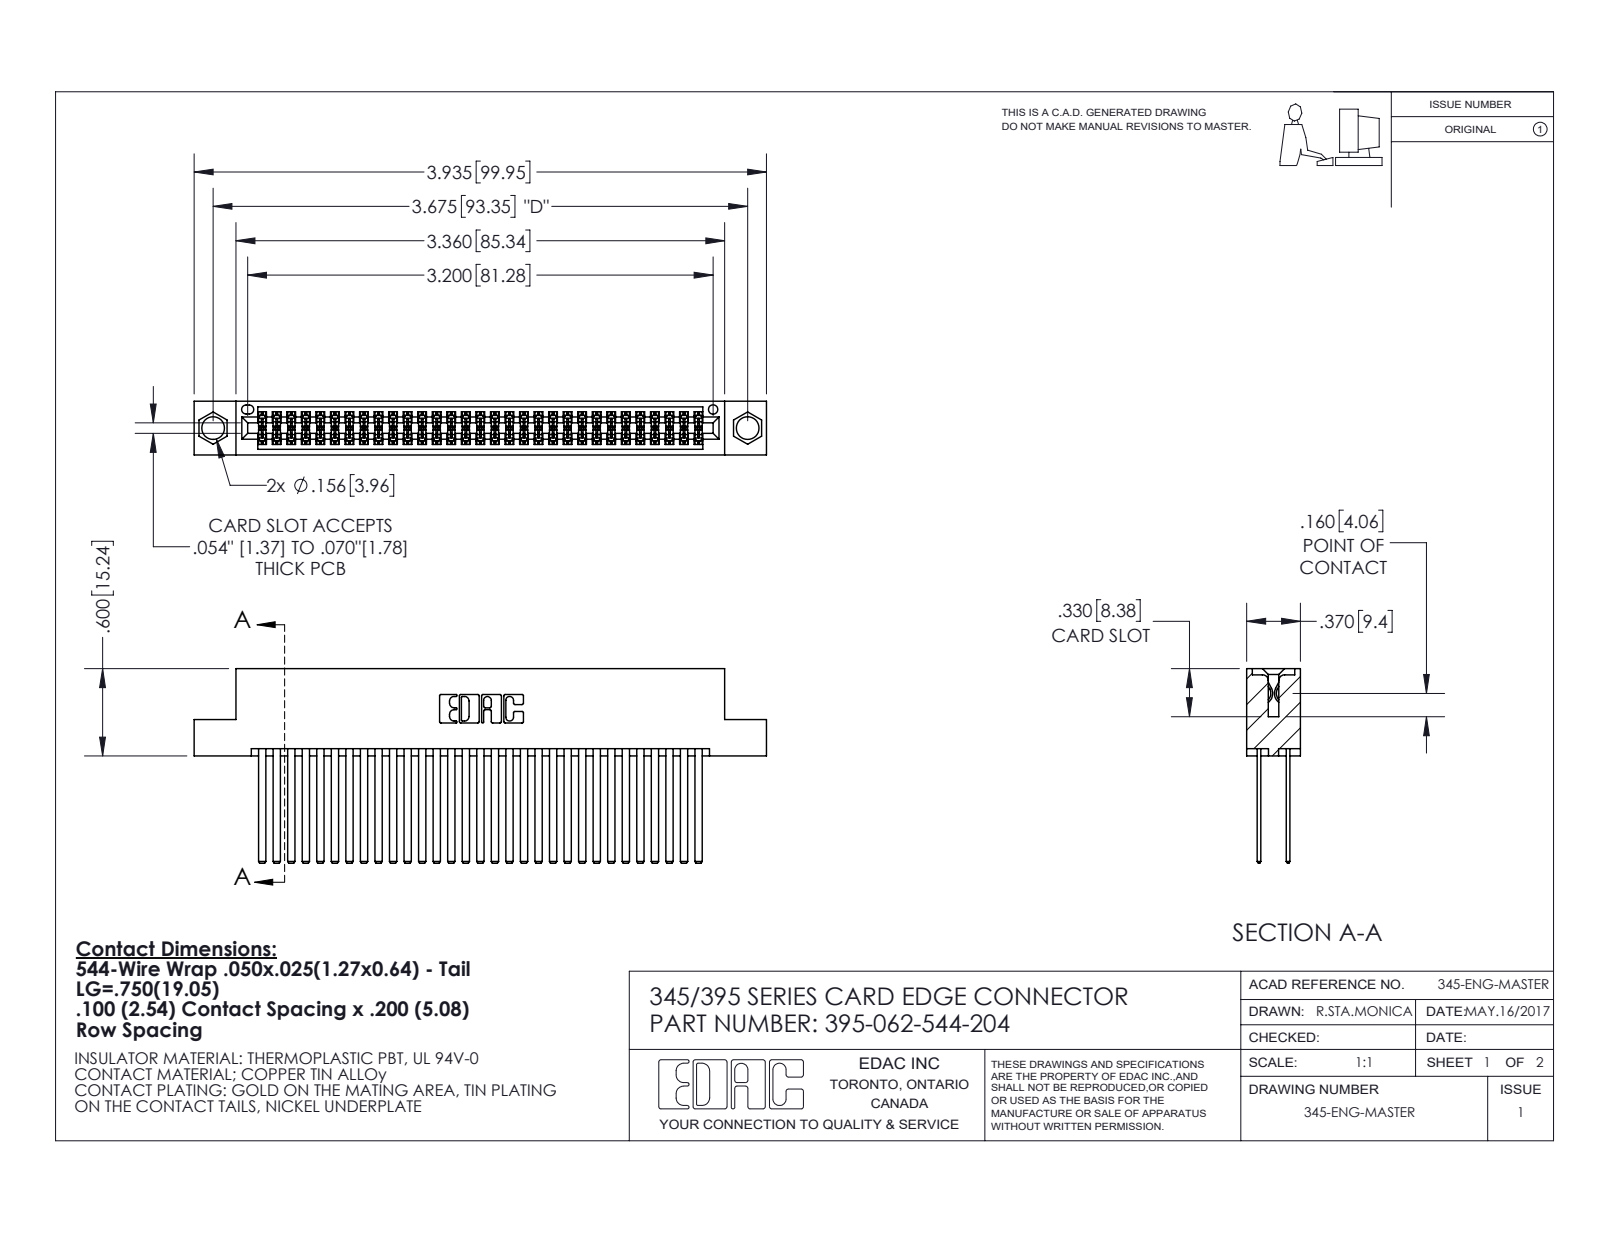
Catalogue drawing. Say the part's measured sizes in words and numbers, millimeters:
The part is named "395-062-544-204; 345-292-001_345-293-144; 345 Part_Flush Mounting Lugs - 0.156 Dia-TI". Its 3-D file was written by "SolidWorks 2020 (CONFIG_CONTROL_DESIGN)". It is 63 solids with 2868 faces: 1892 planar, 976 cylindrical and 0 other. Overall it measures 99.9 by 34 by 9.4 millimeters. Its volume is 10 400 cubic millimeters and its surface area 17 520 square millimeters. Round holes: 2 of diameter 4, 1 of diameter 1.6. Partial cylindrical surfaces (rounded edges, fillets, slot ends): 124 of radius 0.2, 22 of radius 0.3, 6 of radius 0.2, 6 of radius 0.8, 3 of radius 0.7, 2 of radius 0.4, 2 of radius 0.5, 2 of radius 0.6. The main face-to-face distances are 5.1, 0.6, 1.8, 7.6, 2.5, 6.9, 5.7, 4.4, 9.4, 1.3. The hole center spacings are 6.9, 87.4, 93.3.
